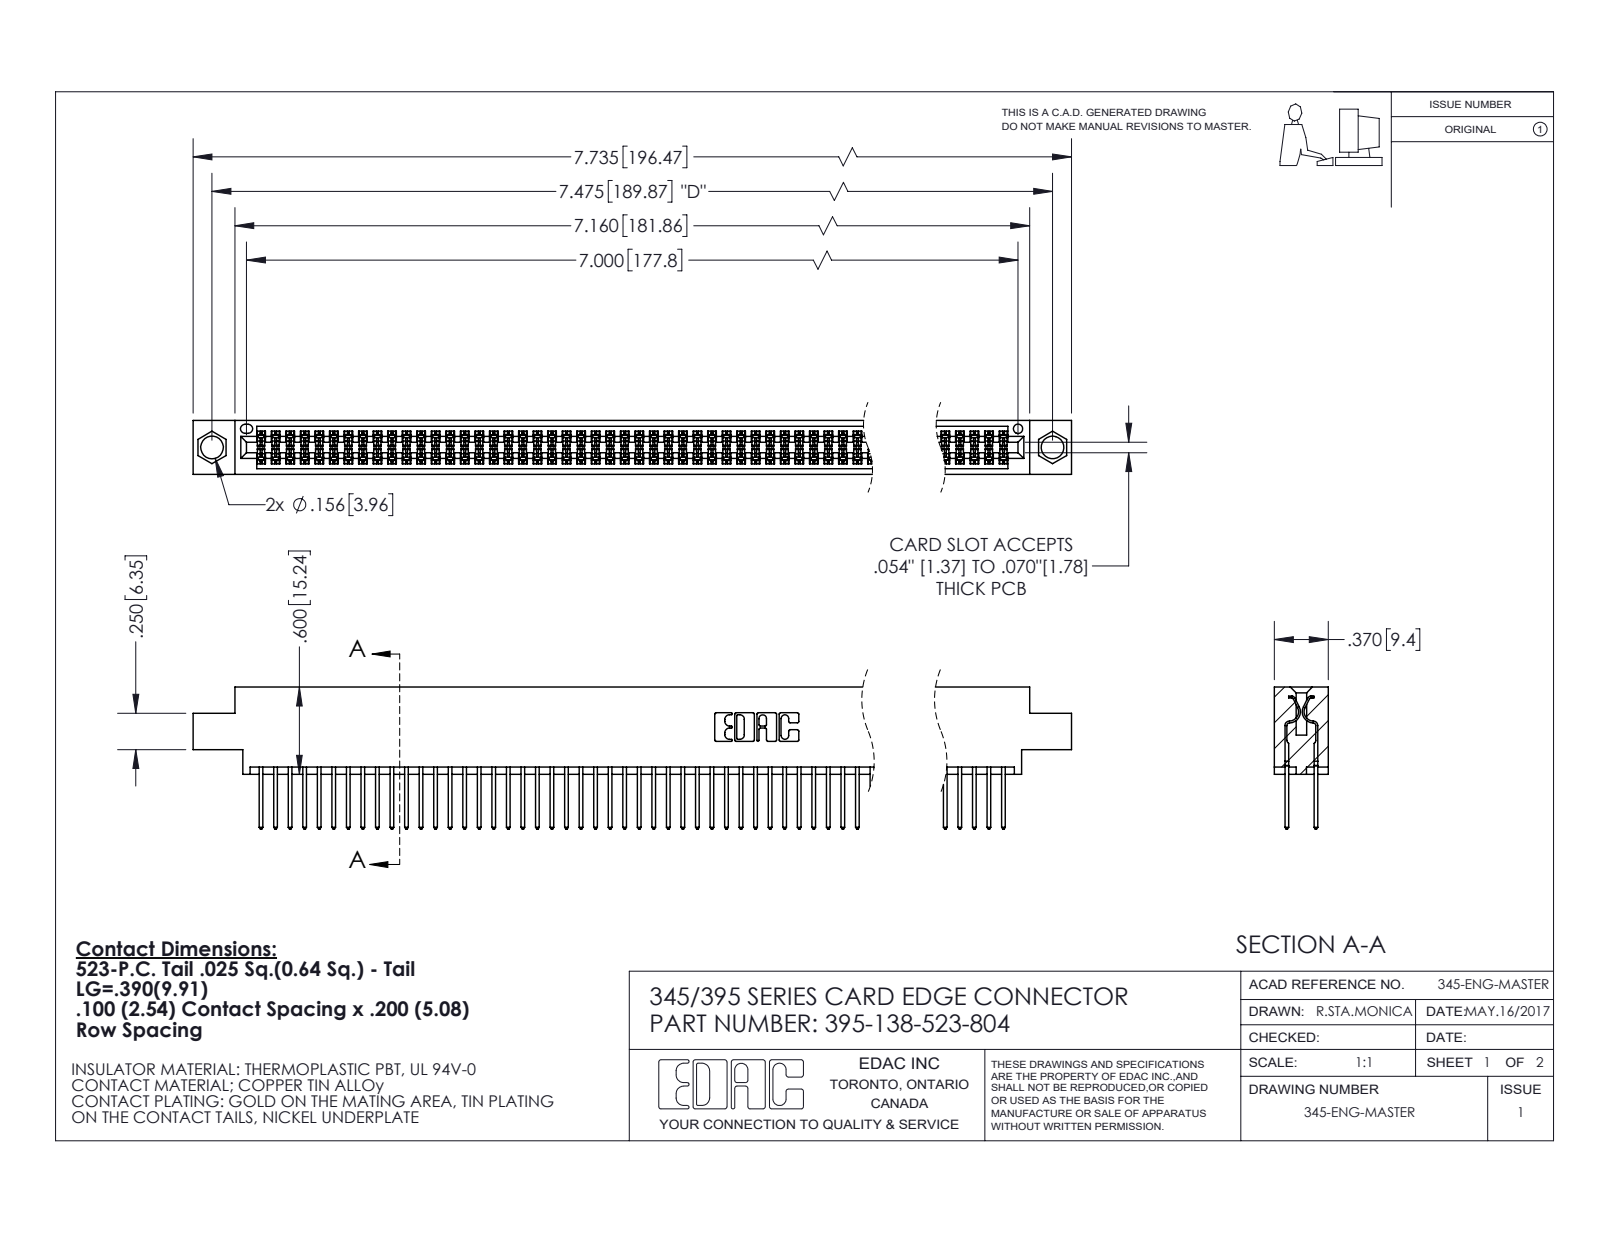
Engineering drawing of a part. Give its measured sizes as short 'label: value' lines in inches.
name: 345-292-001_345-293-123; 345 Part_0.170 Offset - 0.156 Dia-TI; 395-138-523-804
written by: SolidWorks 2020 (CONFIG_CONTROL_DESIGN)
unit: in
bodies: 139 solids, 7044 faces (4652 planar, 2392 cylindrical, 0 other)
size: 7.735 × 0.977 × 0.37
volume: 1.184 in³; area: 47.22 in²
holes: 2× ⌀0.156, 1× ⌀0.064
rounds: 276× R0.006, 138× R0.01, 22× R0.01, 6× R0.007, 6× R0.031, 3× R0.026, 2× R0.014, 2× R0.019
face distances: 0.072, 0.298, 0.2, 0.098, 0.272, 0.025, 0.37, 0.225, 0.175, 0.149
hole spacings: 0.27, 7.239, 7.475
